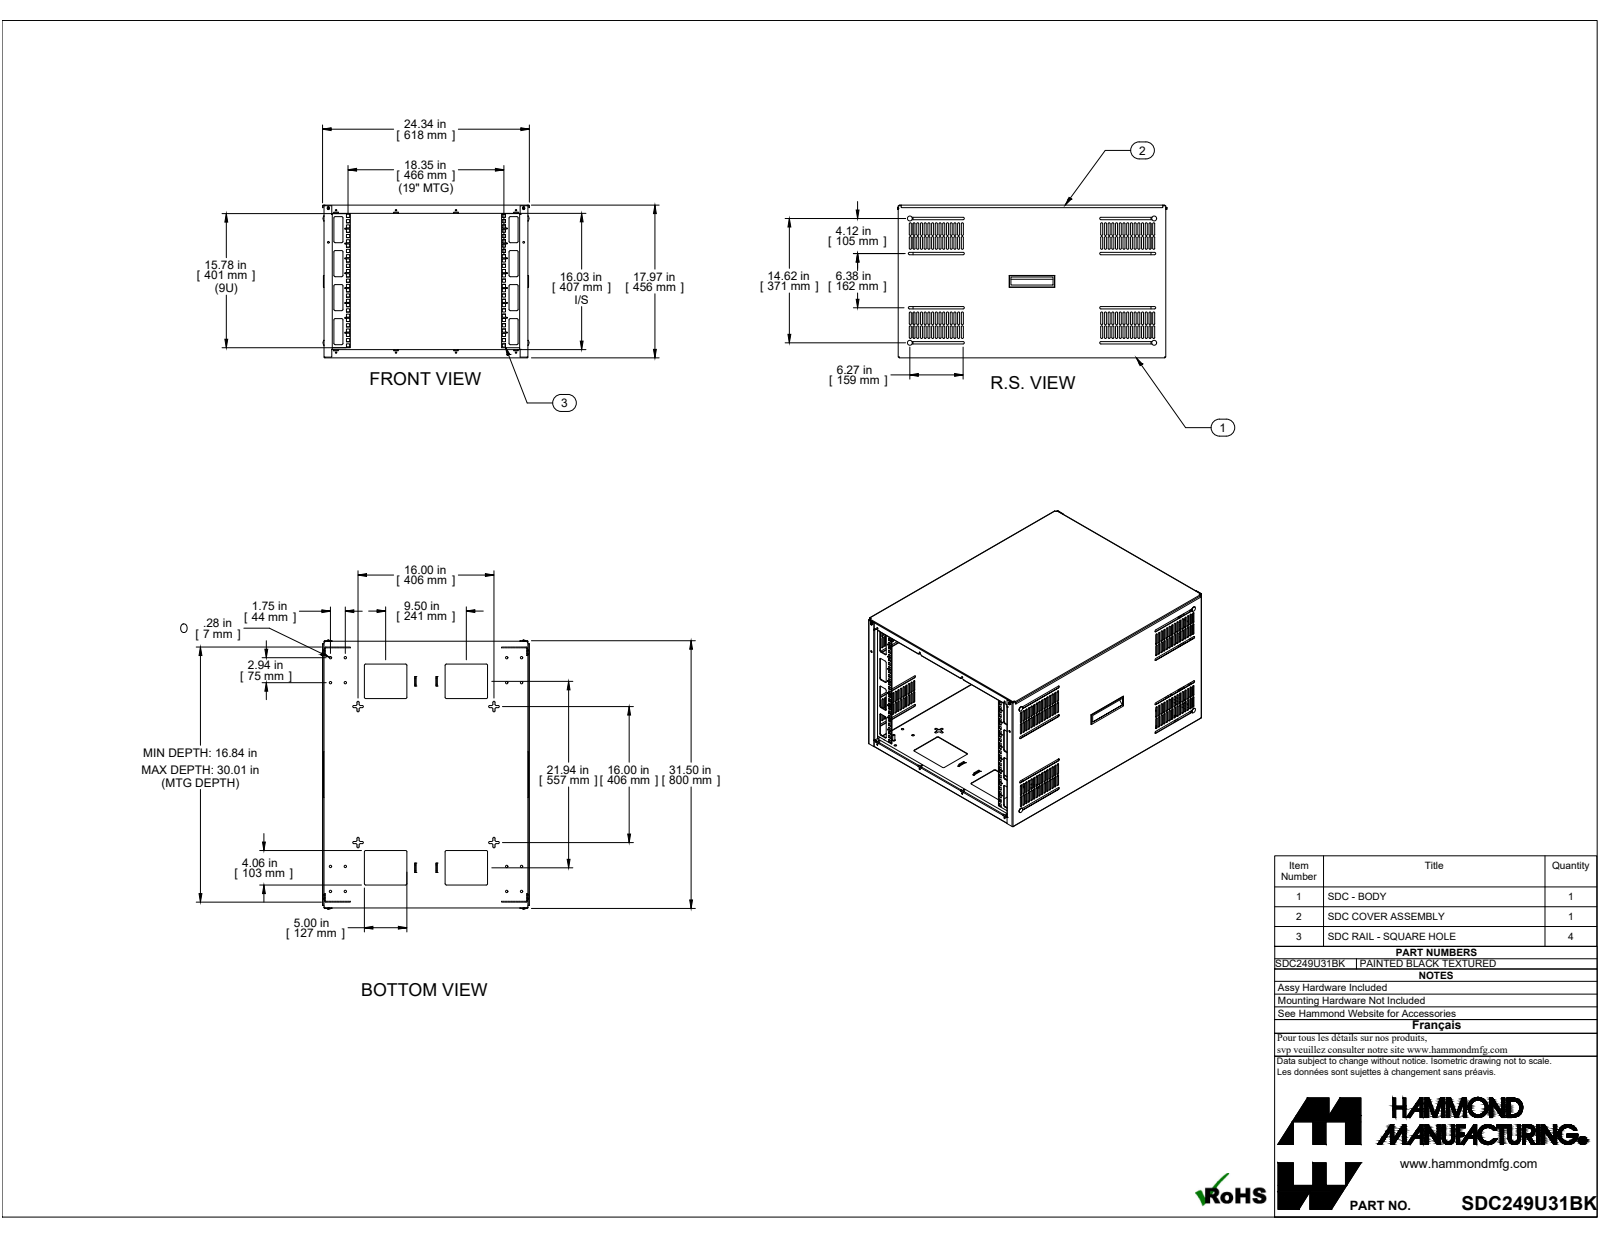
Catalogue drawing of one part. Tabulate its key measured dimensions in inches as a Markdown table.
| quantity | value |
| --- | --- |
| part name | SDC249U31BK |
| STEP written by | SolidWorks 2019 (CONFIG_CONTROL_DESIGN) |
| units | inches |
| bodies | 37 solids, 2820 faces (1798 planar, 970 cylindrical, 52 other) |
| overall size | 31.67 × 24.344 × 17.972 |
| volume | 179.7 in³ |
| surface area | 6 108 in² |
| round holes (diameter × count) | 0.125 × 32, 0.17 × 16, 0.281 × 16, 0.196 × 4, 0.159 × 2, 0.187 × 2, 0.213 × 2 |
| round bosses / shafts (diameter × count) | 0.25 × 8, 0.58 × 4, 0.313 × 2, 0.28 × 2, 0.187 × 2, 0.138 × 2 |
| partial cylindrical surfaces (radius × count) | 0.118 × 240, 0.157 × 68, 0.029 × 22, 0.086 × 22, 0.025 × 16, 0.117 × 16, 0.125 × 16, 0.141 × 16 |
| main face-to-face distances | 0.057, 17.915, 23.943, 17.858, 17.972, 23.886, 24, 0.072, 0.912, 0.095 |
| hole center spacings | 1.75, 19.085, 3.5, 5.25, 19.005, 2.937, 3.419, 7 |
